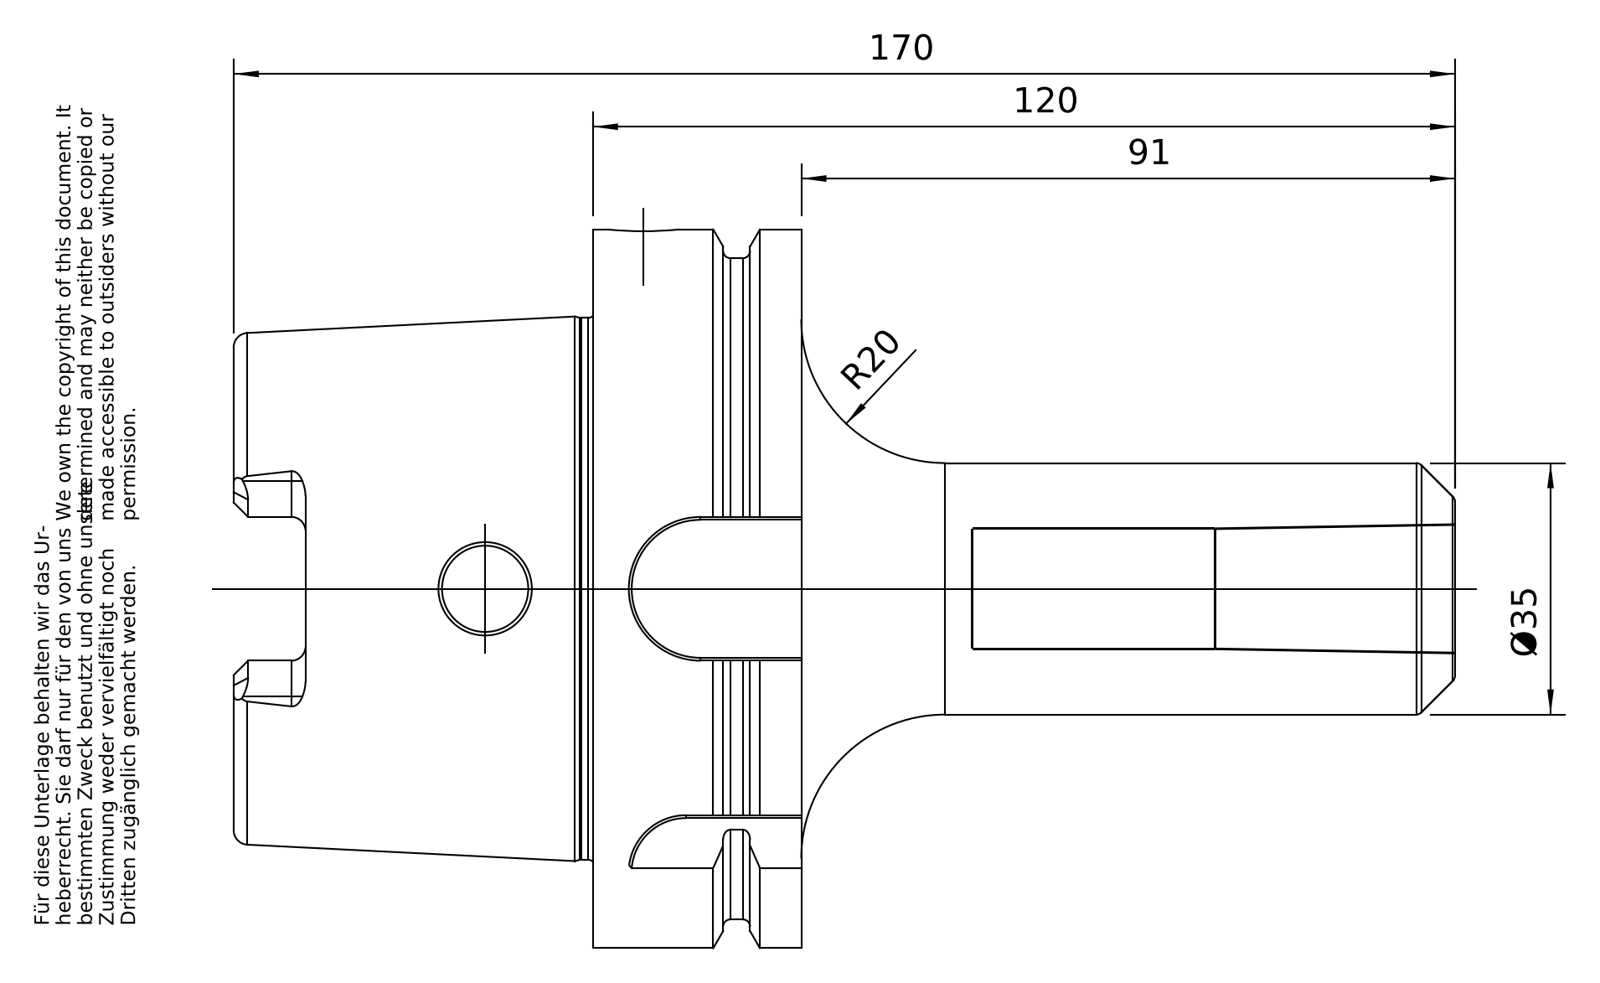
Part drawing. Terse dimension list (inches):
name: A100-120-02
written by: PRO/ENGINEER BY PARAMETRIC TECHNOLOGY CORPORATION, 2010430 (CONFIG_CONTROL_DESIGN)
unit: in
bodies: 1 solid, 178 faces (50 planar, 51 cylindrical, 77 other)
size: 6.693 × 3.937 × 3.937
volume: 20.57 in³; area: 97.14 in²
holes: 1× ⌀0.394, 1× ⌀0.472, 1× ⌀0.658, 1× ⌀0.886, 1× ⌀0.945, 1× ⌀0.957, 1× ⌀0.965, 1× ⌀2.087, 1× ⌀2.48
bosses: 1× ⌀3.937, 1× ⌀3.622, 1× ⌀2.967, 1× ⌀1.378
rounds: 6× R0.079, 4× R0.197, 1× R0.315, 1× R0.394, 1× R0.433
face distances: 1.142, 0.492, 0.65, 1.969, 2.461, 3.11, 3.465, 3.091, 1.122, 0.63
